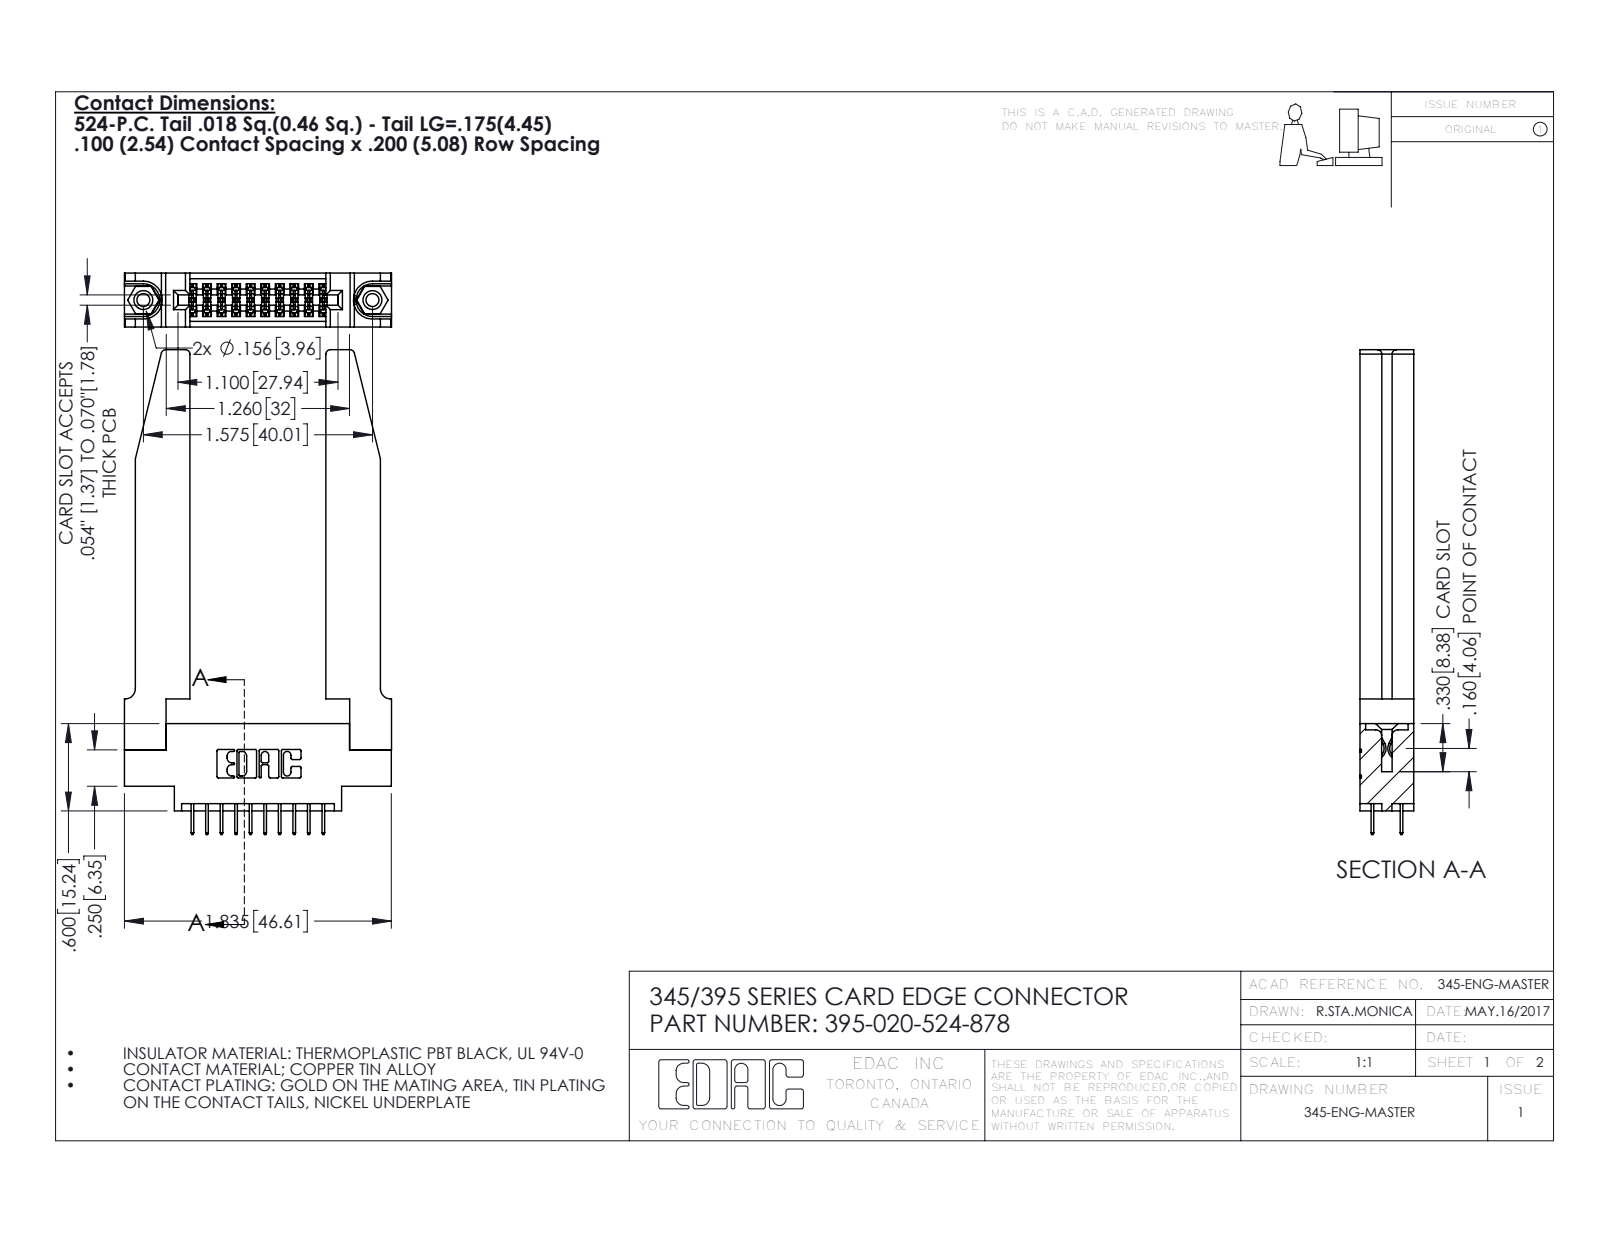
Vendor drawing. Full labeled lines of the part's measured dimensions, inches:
Part name (STEP PRODUCT): 345 Part_0.170 Offset - 0.156 Dia-TH; 345-220-078_345-220-078; 345-250-001_345-250-001-102; 345-292-001_345-293-124 (+1 more)
STEP written by: SolidWorks 2016 (CONFIG_CONTROL_DESIGN)
Units: inches
Bodies: 25 solids, 1444 faces (1006 planar, 386 cylindrical, 52 other)
Overall size (bounding box): 3.332 × 1.836 × 0.37
Volume: 0.724 in³ · Surface area: 19.11 in²
Round holes (diameter × count): ⌀0.089 ×2, ⌀0.125 ×2, ⌀0.156 ×2, ⌀0.064 ×1
Round bosses / shafts (diameter × count): ⌀0.155 ×2
Partial cylindrical surfaces — rounded edges, fillets, slot ends (radius × count): R0.006 ×30, R0.01 ×22, R0.03 ×8, R0.007 ×6, R0.031 ×6, R0.026 ×3, R0.014 ×2, R0.019 ×2
Main face-to-face distances: 0.37, 0.072, 0.298, 0.148, 0.15, 0.22, 0.077, 0.935, 0.2, 0.095
Hole centre spacings: 0.27, 1.344, 1.575
